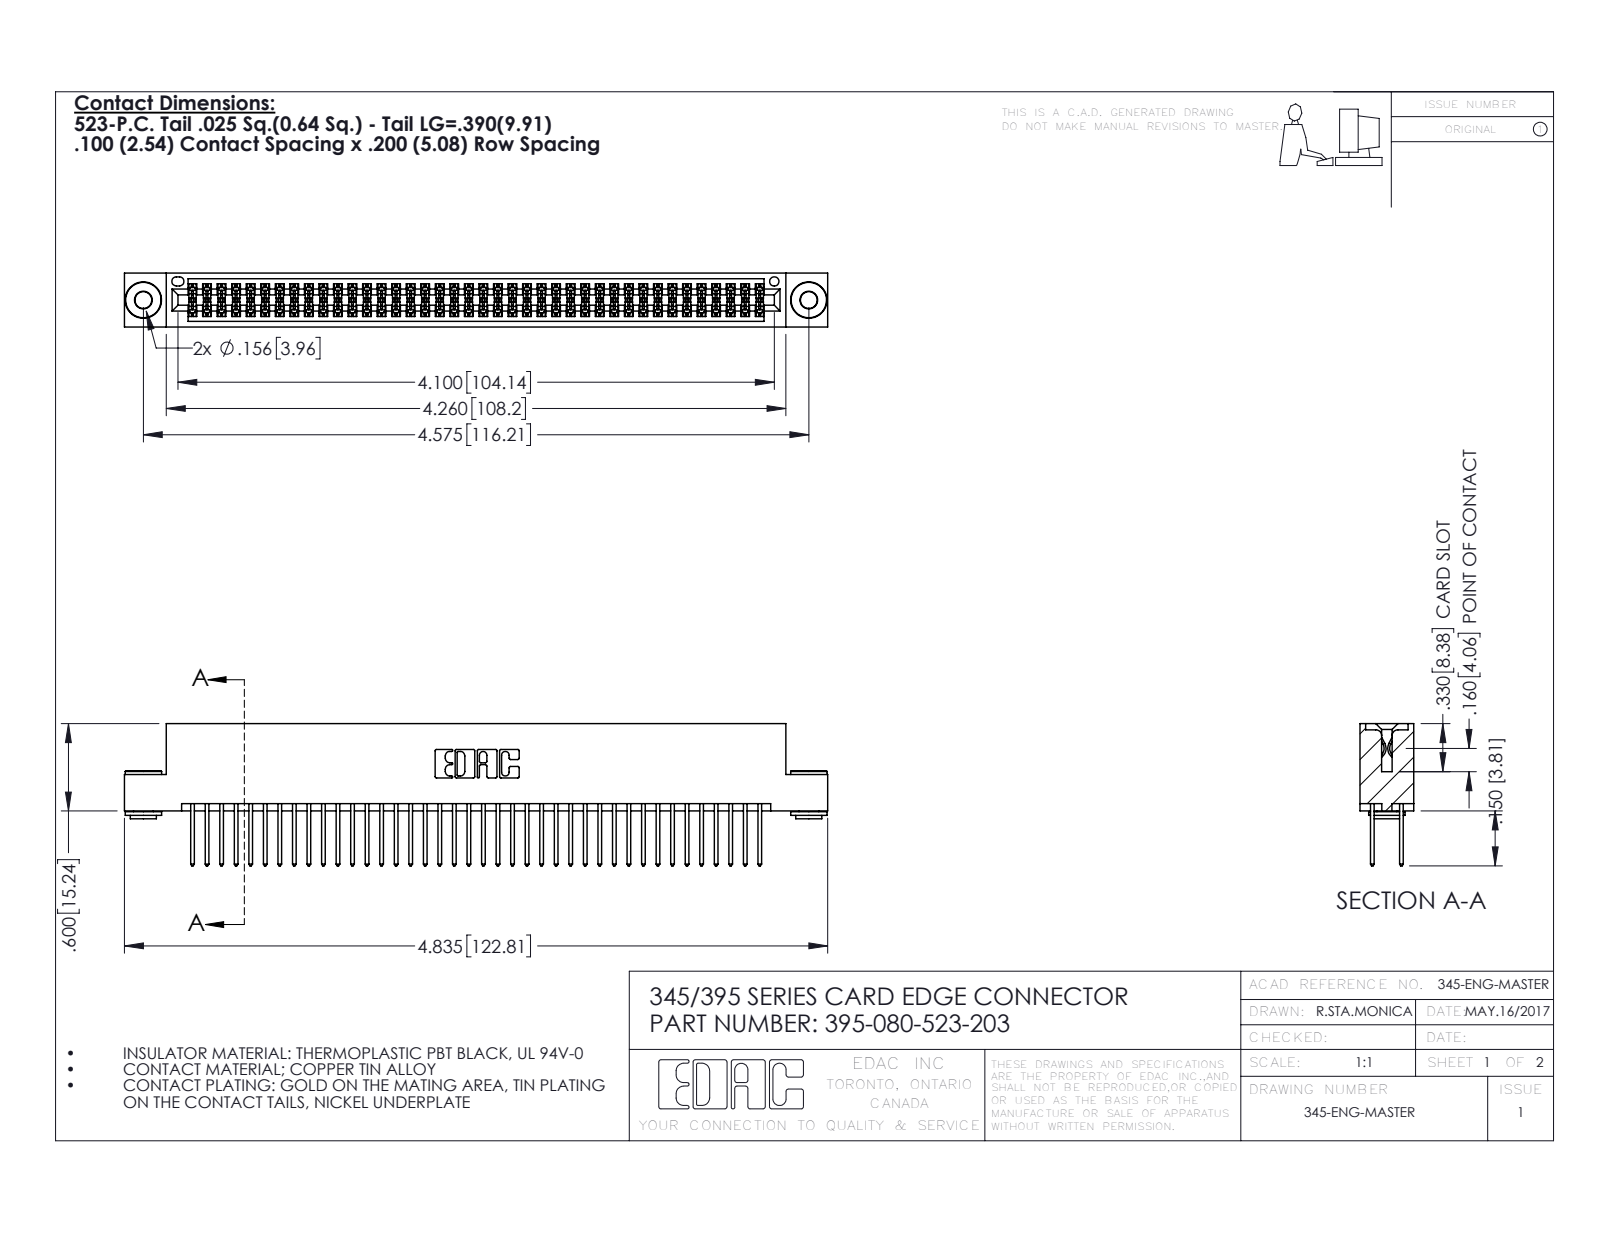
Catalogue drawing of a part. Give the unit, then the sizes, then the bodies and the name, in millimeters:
Units: millimetres
Overall size (bounding box): 122.8 × 24.8 × 9.4
Round holes (diameter × count): ⌀2.9 ×2, ⌀4 ×2, ⌀1.6 ×1
Round bosses / shafts (diameter × count): ⌀6.4 ×2, ⌀4.6 ×2, ⌀3.5 ×2
Partial cylindrical surfaces — rounded edges, fillets, slot ends (radius × count): R0.2 ×120, R0.3 ×80, R0.3 ×22, R0.2 ×6, R0.8 ×6, R0.7 ×3, R0.4 ×2, R0.5 ×2
Main face-to-face distances: 1.8, 7.6, 5.1, 0.6, 2.5, 6.9, 9.4, 5.7, 4.4, 3.8
Hole centre spacings: 6.9, 110.2, 116.2
Volume: 12 100 mm³ · Surface area: 18 780 mm²
Bodies: 83 solids, 4164 faces (2730 planar, 1426 cylindrical, 8 other)
Part name (STEP PRODUCT): 345-250-002_345-250-002-102; 345 Part_Flush Mounting Lugs - 0.156 Dia-TH; 395-080-523-203; 345-292-001_345-293-123
STEP written by: SolidWorks 2016 (CONFIG_CONTROL_DESIGN)
